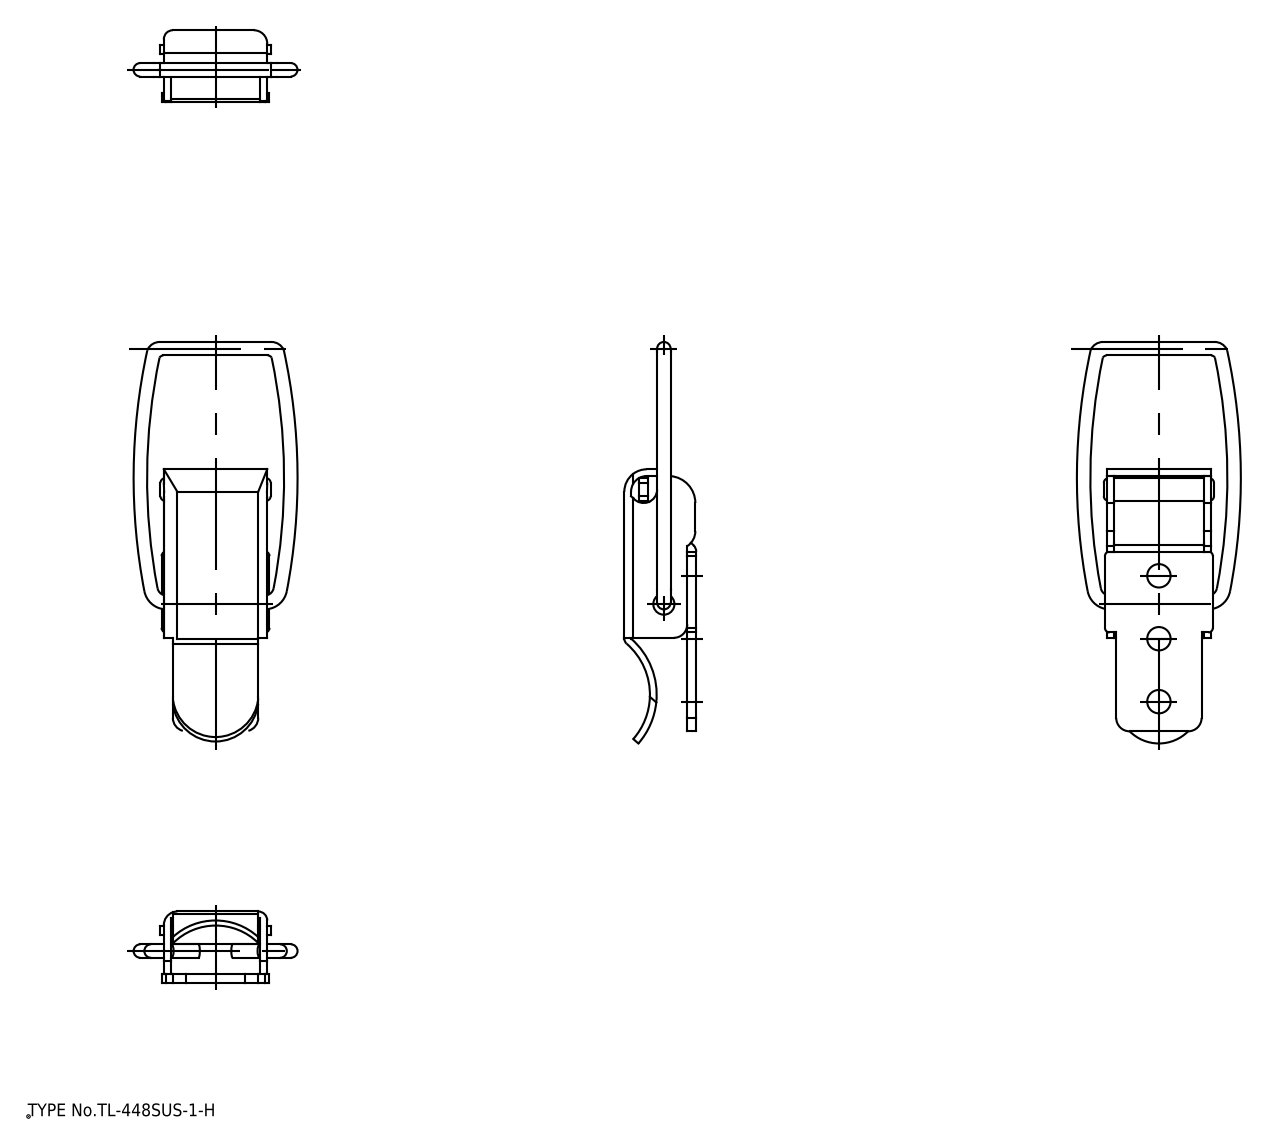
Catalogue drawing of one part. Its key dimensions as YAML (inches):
part_name: "アーム; ベース; レバー"
step_written_by: "spGate 20.6.3 (****-****-****-****) (AUTOMOTIVE_DESIGN)"
units: inches
bodies: {solids: 3, faces: 120, planar: 55, cylindrical: 46, other: 19}
overall_size: [3.517, 1.436, 0.63]
volume: 0.418
surface_area: 14.31
round_holes:
  - {diameter: 0.205, count: 3}
  - {diameter: 0.185, count: 1}
round_bosses_or_shafts:
  - {diameter: 0.118, count: 1}
partial_cylinders:
  - {radius: 0.039, count: 8}
  - {radius: 0.059, count: 5}
  - {radius: 0.118, count: 5}
  - {radius: 0.079, count: 4}
  - {radius: 0.138, count: 1}
  - {radius: 0.157, count: 1}
  - {radius: 0.197, count: 1}
  - {radius: 0.236, count: 1}
face_to_face_distances: [0.059, 0.079, 0.846, 0.492, 0.571, 0.63, 0.551, 0.787, 0.906, 0.421]
hole_center_spacings: [0.551, 1.102]
